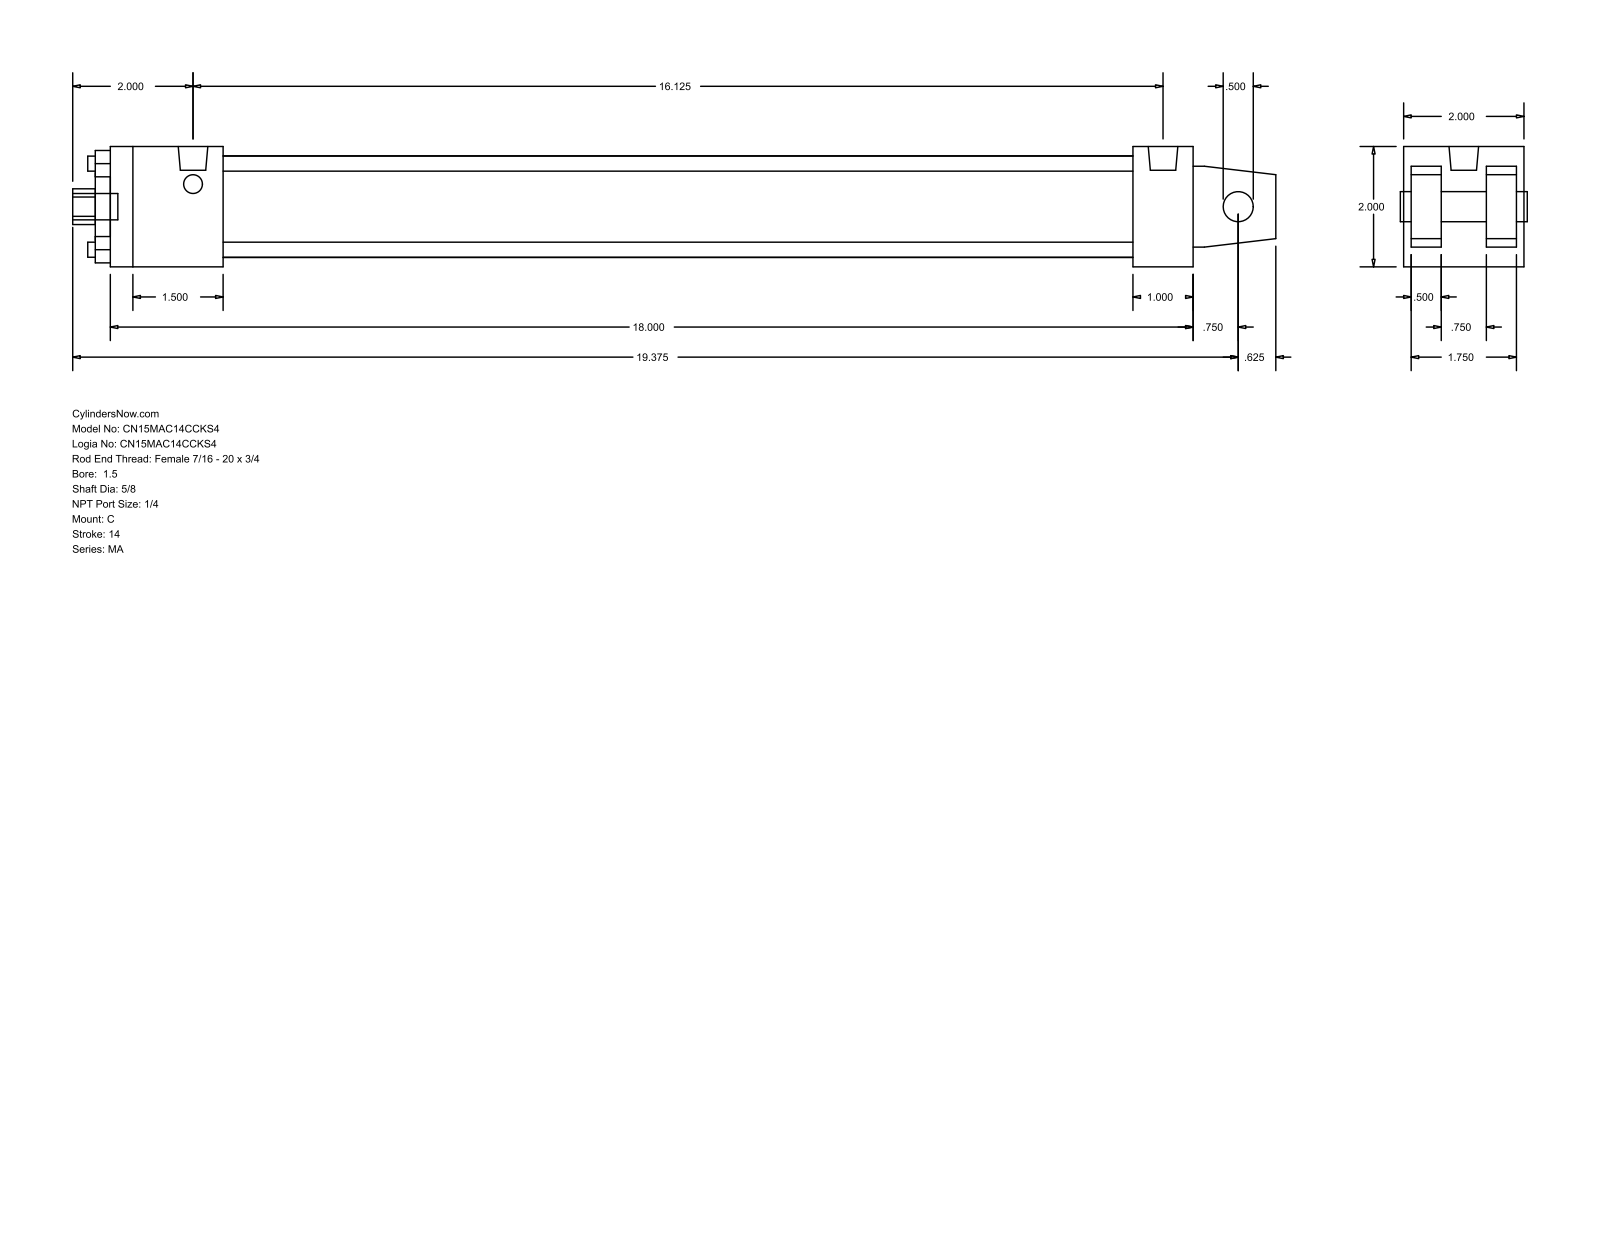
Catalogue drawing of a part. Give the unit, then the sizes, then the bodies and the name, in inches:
Units: inches
Overall size (bounding box): 20 × 2 × 2
Round holes (diameter × count): ⌀0.25 ×4, ⌀0.5 ×1, ⌀0.625 ×1, ⌀1.125 ×1, ⌀1.69 ×1
Round bosses / shafts (diameter × count): ⌀0.313 ×4, ⌀0.492 ×2, ⌀0.437 ×1
Partial cylindrical surfaces — rounded edges, fillets, slot ends (radius × count): R0.297 ×1
Main face-to-face distances: 2, 1.375, 0.5, 0.125, 0.625, 1.875, 1.25, 18, 17, 1
Hole centre spacings: 1.011, 1.43, 2.022
Bodies: 0 solids, 103 faces (76 planar, 27 cylindrical, 0 other)
Part name (STEP PRODUCT): MA_C__0150_0.625
STEP written by: GSSL Pune (CONFIG_CONTROL_DESIGN)
